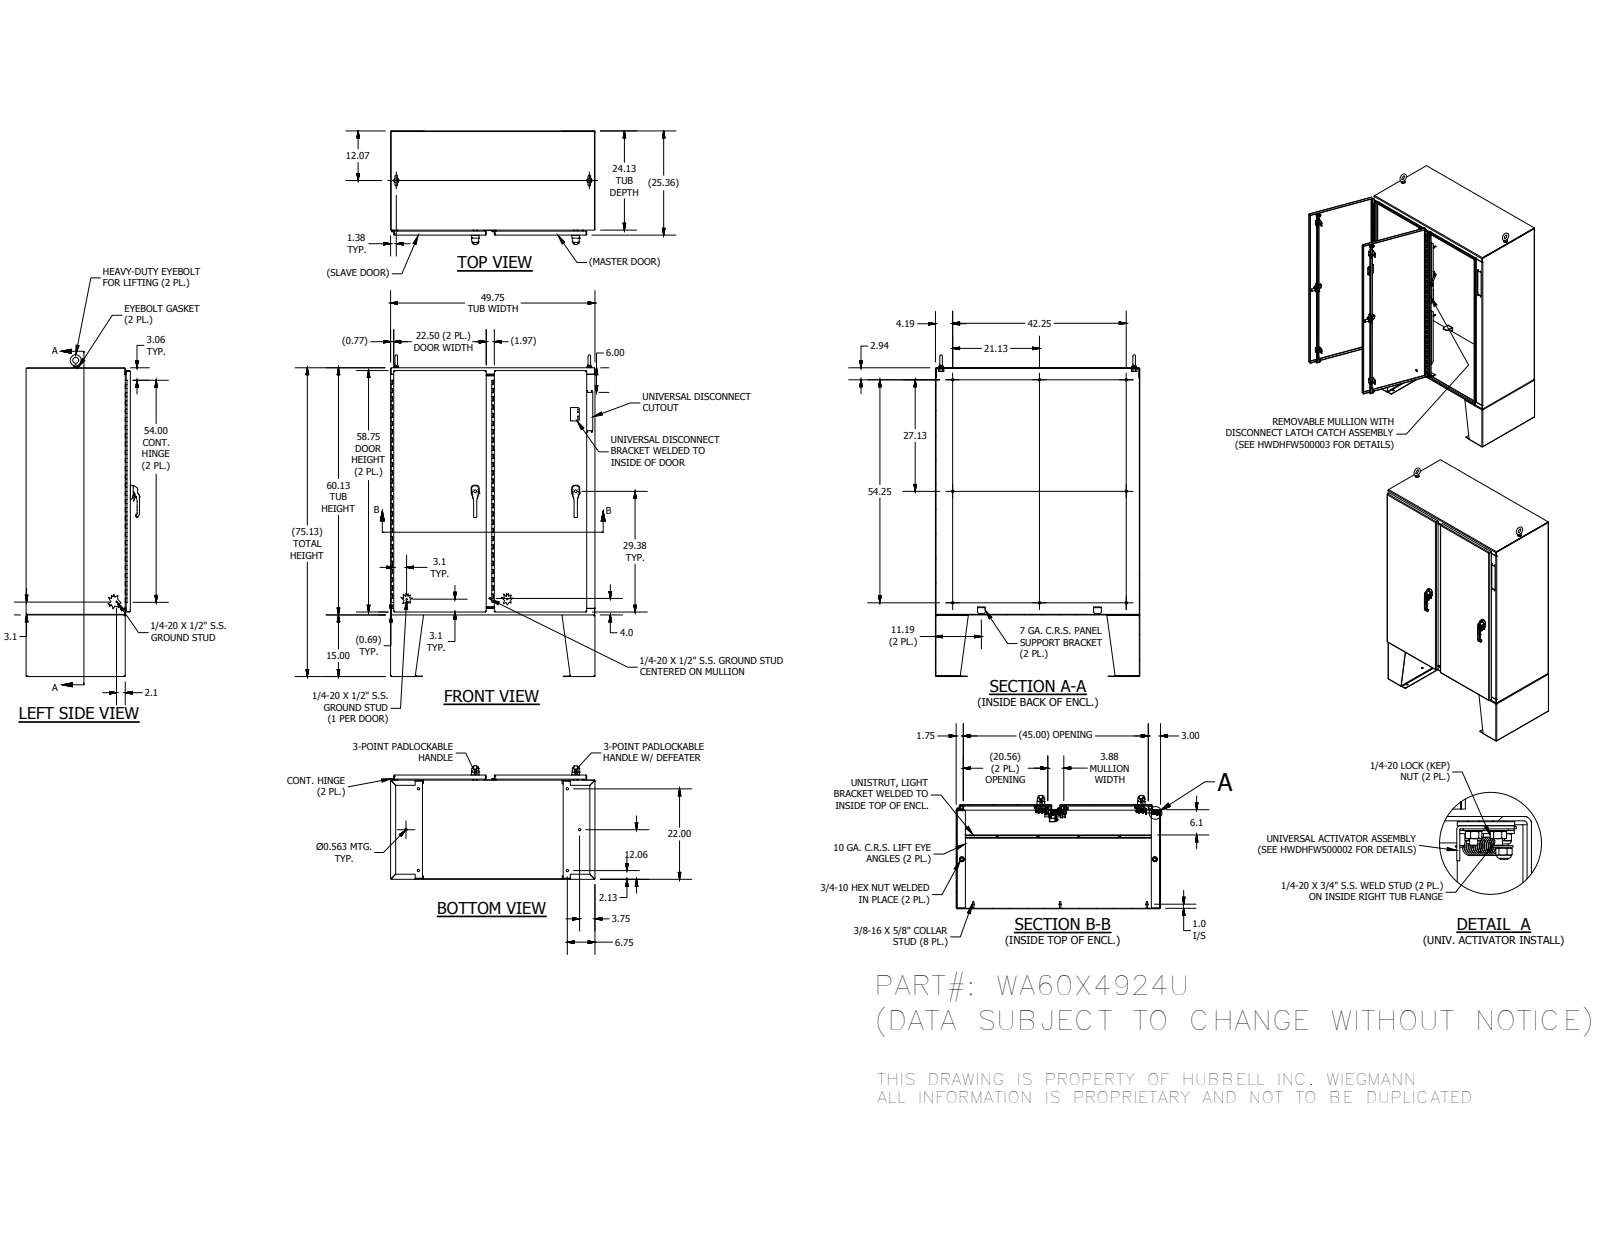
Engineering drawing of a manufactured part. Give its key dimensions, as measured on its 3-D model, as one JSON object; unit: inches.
{"part_name": "WA60X4924UBLR; WAX4924UTOP; WAX4924UBTM; HFW332010S (+8 more)", "step_written_by": "Autodesk Inventor 2016 (AUTOMOTIVE_DESIGN)", "units": "inches", "bodies": {"solids": 212, "faces": 8687, "planar": 3990, "cylindrical": 2936, "other": 1761}, "overall_size": [78.248, 49.75, 27.608], "volume_in3": 1969, "surface_area_in2": 30600, "round_holes": [[0.25, 18], [0.375, 18], [0.563, 18], [0.19, 8], [0.2, 8], [0.203, 8], [0.276, 8], [0.289, 8], [0.313, 8], [0.335, 8], [0.38, 8], [0.201, 7]], "round_bosses_or_shafts": [[0.25, 24], [0.33, 18], [0.625, 13], [0.337, 12], [0.375, 11], [0.563, 9], [1, 8], [0.438, 8]], "partial_cylinders_radius": [[0.02, 333], [0.012, 203], [0.02, 192], [0.019, 42], [0.05, 40], [0.125, 37], [0.094, 35], [0.063, 27]], "face_to_face_distances": [0.134, 0.134, 25.217, 49.616, 25.083, 25.35, 59.991, 49.482, 49.75, 0.125], "hole_center_spacings": [0.024, 2, 24.469, 0.025, 24.485, 1.102, 1.102, 1.601]}
